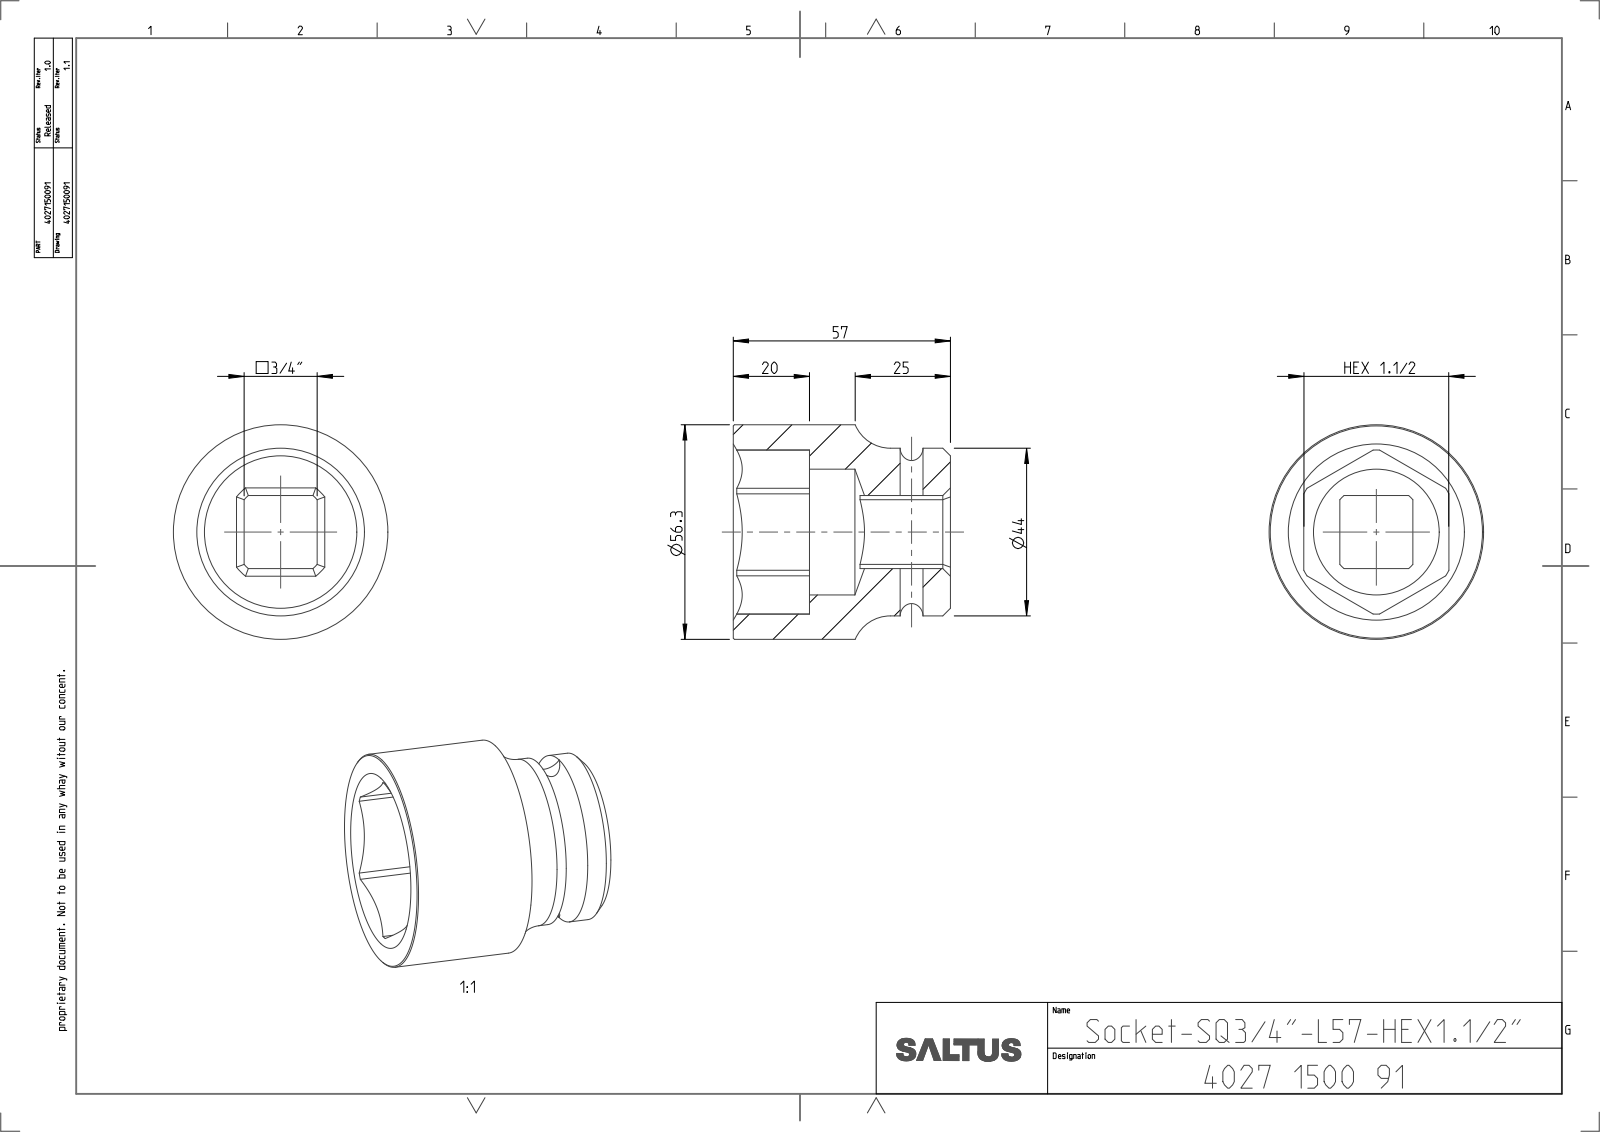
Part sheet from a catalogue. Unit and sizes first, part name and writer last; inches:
Units: inches
Overall size (bounding box): 2.244 × 2.217 × 2.217
Round holes (diameter × count): ⌀0.236 ×1, ⌀1.299 ×1
Round bosses / shafts (diameter × count): ⌀2.217 ×1, ⌀1.732 ×1
Partial cylindrical surfaces — rounded edges, fillets, slot ends (radius × count): R0.504 ×1, R0.848 ×1
Main face-to-face distances: 1.5, 2.244, 0.372, 1.128, 0.755, 1.457, 0.787
Volume: 4.385 in³ · Surface area: 28.93 in²
Bodies: 1 solid, 55 faces (17 planar, 22 cylindrical, 16 other)
Part name (STEP PRODUCT): 4027150091
STEP written by: CREO PARAMETRIC BY PTC INC, 2022414 (CONFIG_CONTROL_DESIGN)
